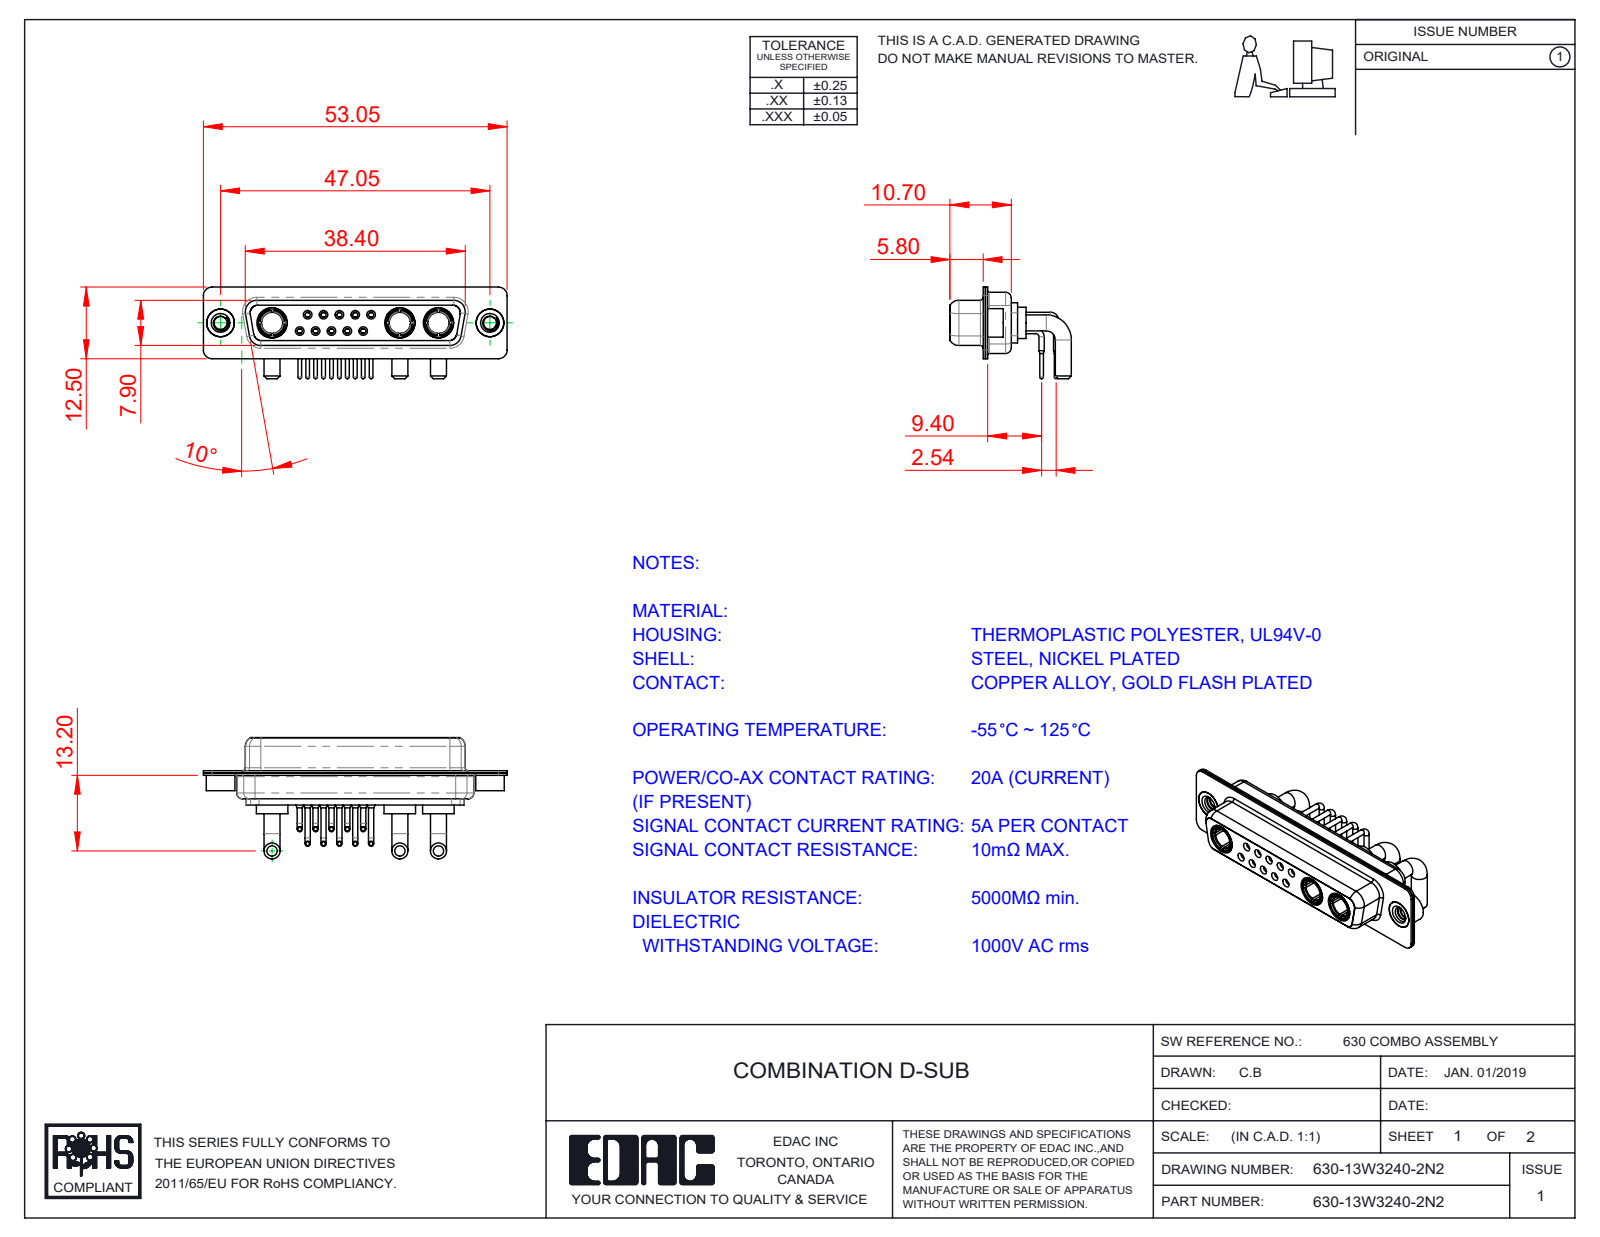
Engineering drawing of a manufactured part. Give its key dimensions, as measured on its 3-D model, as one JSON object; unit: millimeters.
{"part_name": "630Combo Contact Row 2; 630Combo Threaded Rivet_2; 630Combo Contact Row 1; 630Combo Shell Front_25 Contacts (+4 more)", "step_written_by": "SolidWorks 2020 (CONFIG_CONTROL_DESIGN)", "units": "millimeters", "bodies": {"solids": 21, "faces": 1043, "planar": 304, "cylindrical": 442, "other": 297}, "overall_size": [53.05, 21.2, 16], "volume_mm3": 4026, "surface_area_mm2": 9019, "round_holes": [[0.9, 10], [1.1, 10], [1.5, 10], [2, 10], [1.6, 5], [1.7, 5], [4.85, 5], [3.7, 3], [5.3, 3], [2.26, 2], [4, 2], [4.05, 2]], "round_bosses_or_shafts": [[0.9, 10], [0.65, 10], [2.8, 6], [1.6, 5], [5.5, 3], [5.2, 3], [4.96, 3], [4.75, 3]], "partial_cylinders_radius": [[1.5, 16], [2, 12], [1.35, 8], [1.6, 8], [0.25, 4], [0.5, 4], [0.6, 4], [0.65, 4]], "face_to_face_distances": [0.4, 1.4, 0.45, 8.45, 8.9, 1.8, 6.2, 7.05, 7.5, 1.85], "hole_center_spacings": [3.16, 2.77, 5.54, 5.03, 5.04, 8.31, 7.48, 7.49]}
